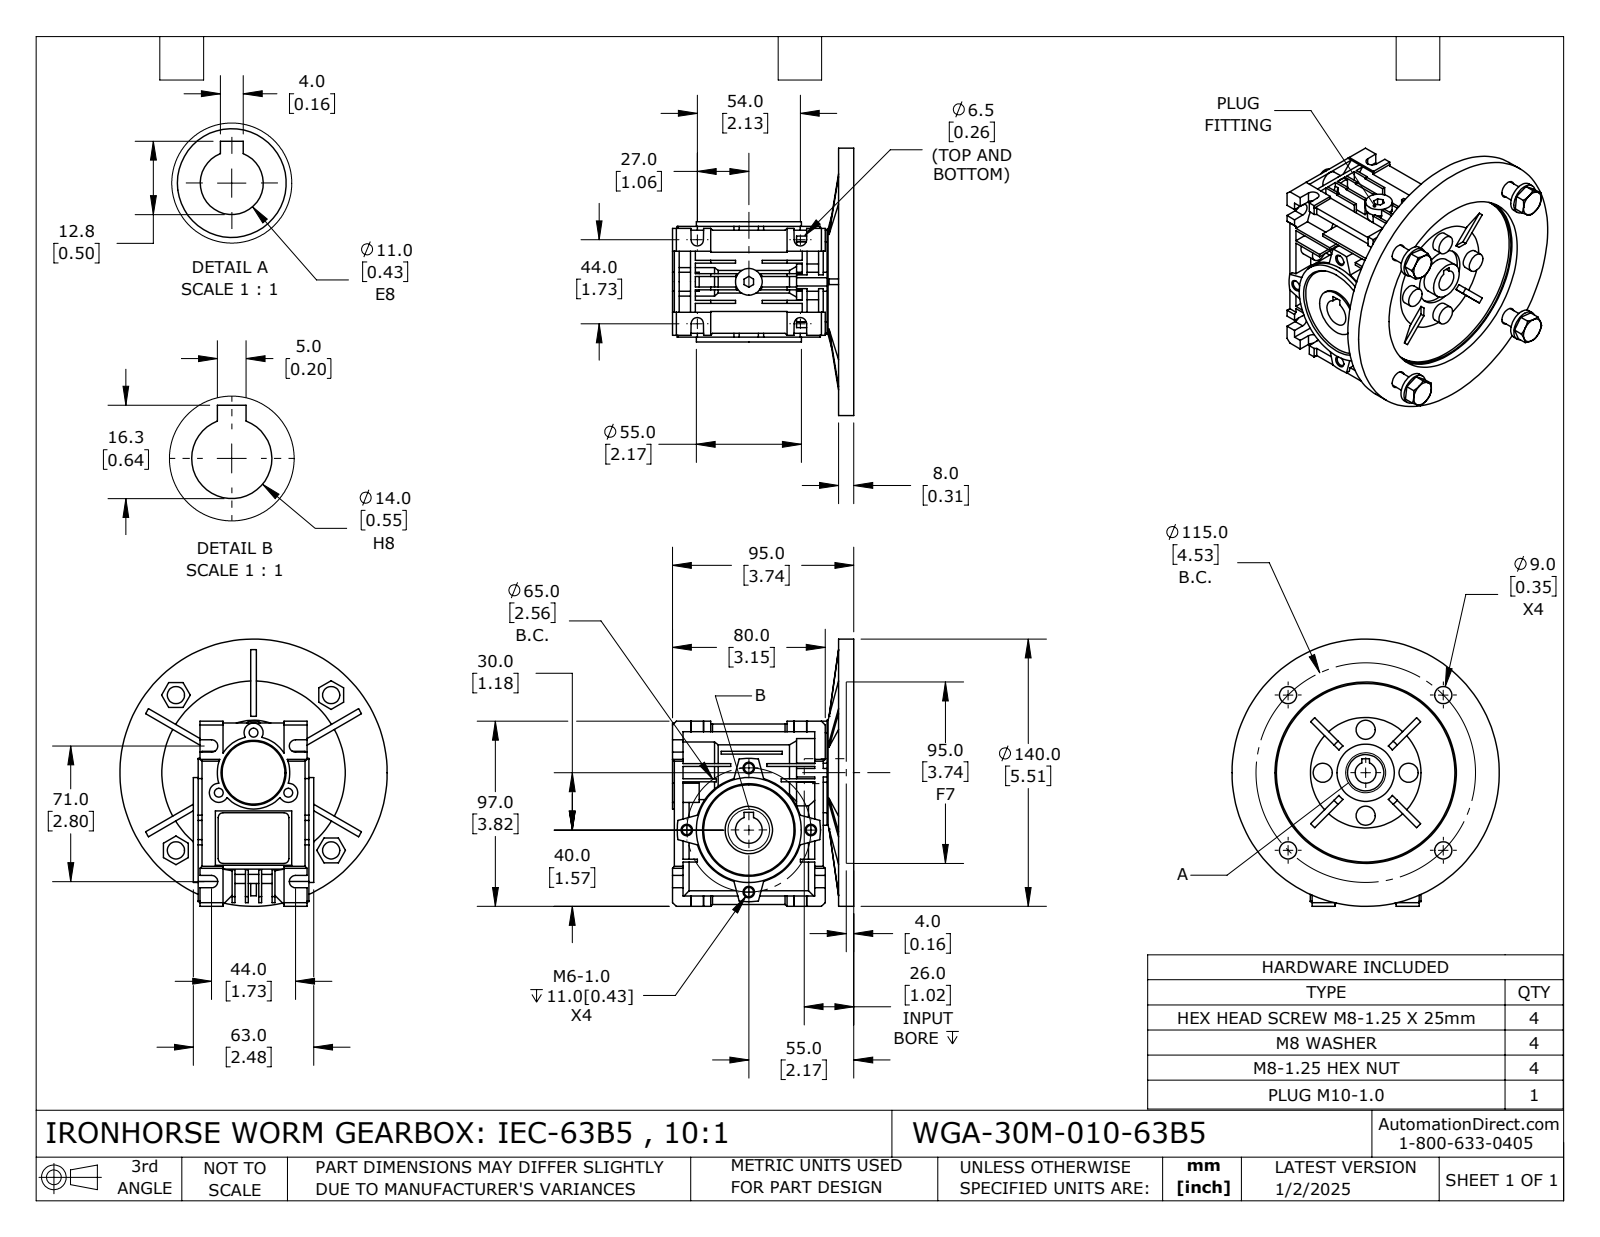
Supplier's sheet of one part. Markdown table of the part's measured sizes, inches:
| quantity | value |
| --- | --- |
| part name | WGA-30M-010-63B5 |
| STEP written by | SolidWorks 2024 (CONFIG_CONTROL_DESIGN) |
| units | inches |
| bodies | 18 solids, 1048 faces (618 planar, 256 cylindrical, 174 other) |
| overall size | 5.512 × 5.512 × 4.448 |
| volume | 24.68 in³ |
| surface area | 217.5 in² |
| round holes (diameter × count) | 0.354 × 5, 0.194 × 4, 0.268 × 4, 0.315 × 4, 0.359 × 4, 0.183 × 3, 0.194 × 2, 0.433 × 1, 0.453 × 1, 0.551 × 1, 0.571 × 1, 0.748 × 1 |
| round bosses / shafts (diameter × count) | 0.63 × 4, 0.394 × 4, 2.165 × 2, 5.512 × 1, 2.205 × 1, 1.496 × 1, 1.457 × 1, 0.551 × 1 |
| partial cylindrical surfaces (radius × count) | 0.128 × 8, 0.098 × 4, 0.197 × 3, 0.295 × 1, 0.669 × 1, 0.846 × 1, 1.476 × 1 |
| main face-to-face distances | 0.059, 0.315, 0.276, 0.217, 0.039, 0.551, 0.157, 0.177, 0.335, 0.079 |
| hole center spacings | 1.28, 1.809, 2.264, 3.202, 0.827, 1.432, 1.481, 1.778 |
